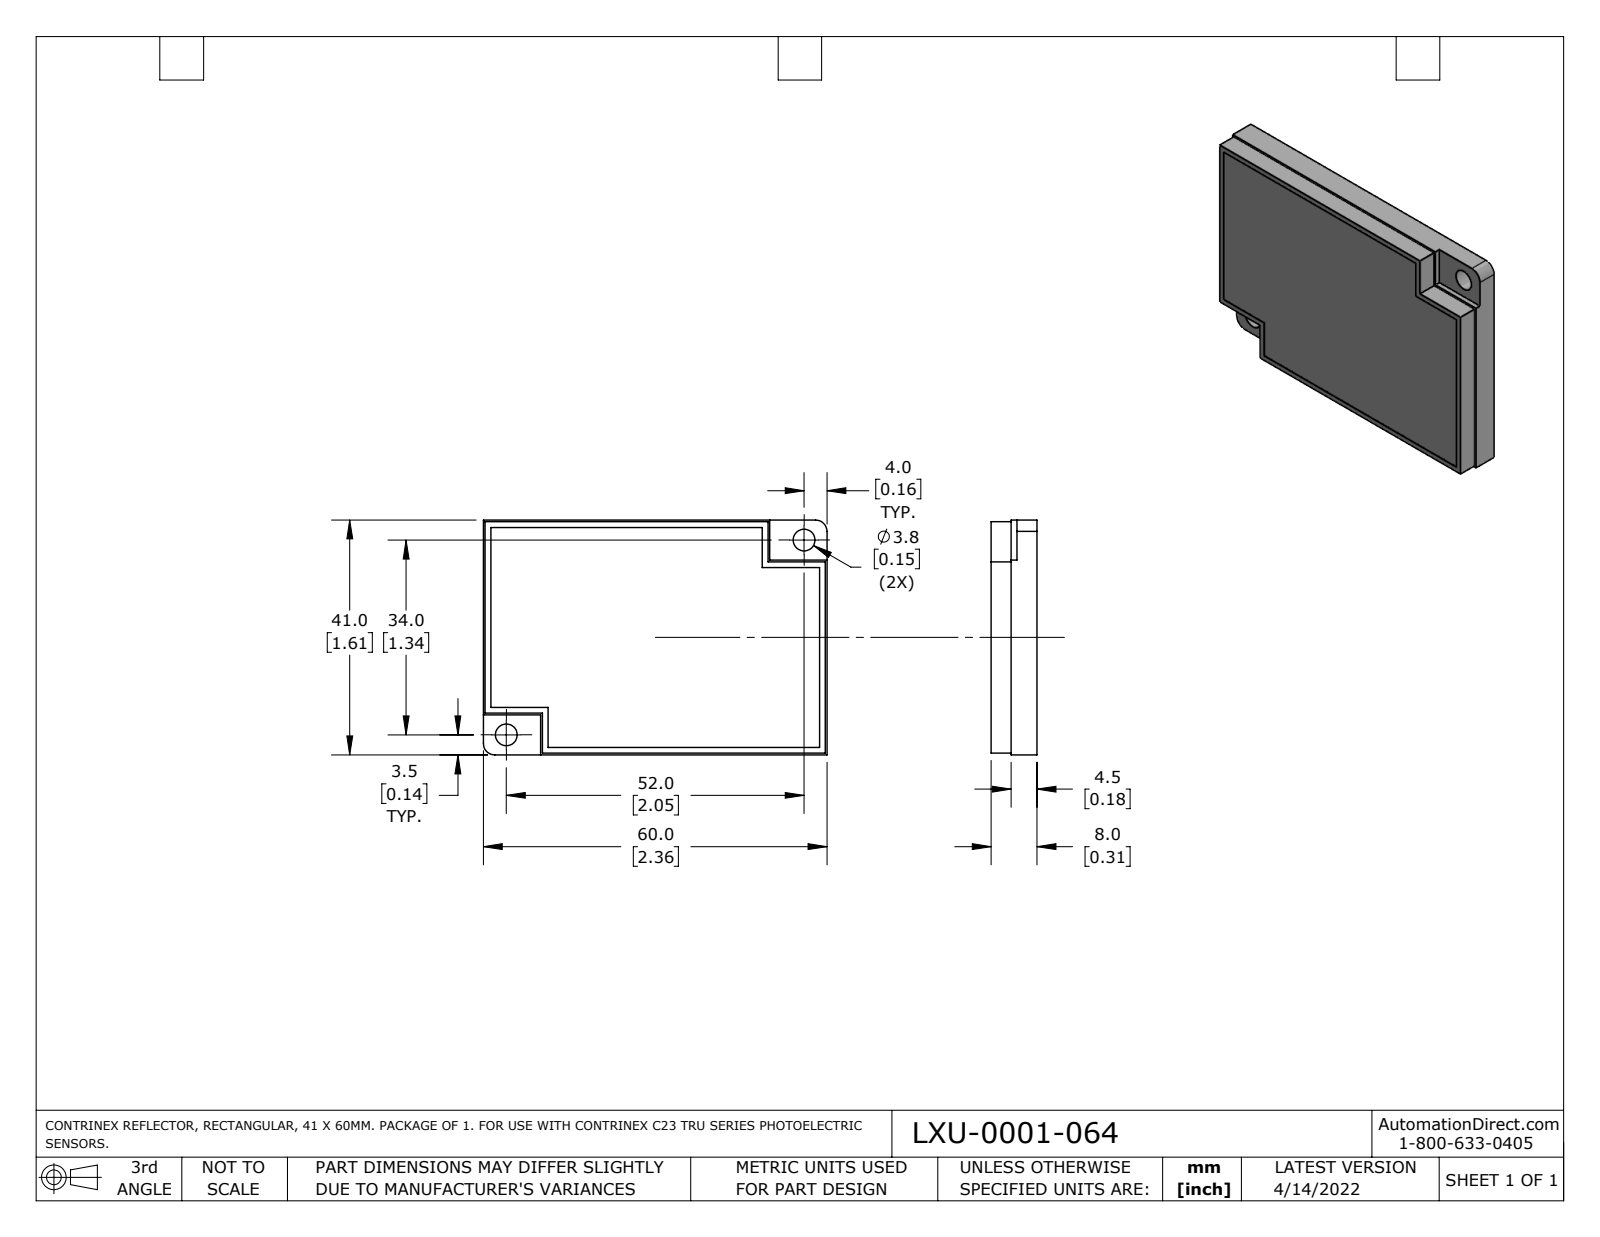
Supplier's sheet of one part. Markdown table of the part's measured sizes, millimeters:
| quantity | value |
| --- | --- |
| part name | LXU-0001-064 |
| STEP written by | PARTsolutions (AUTOMOTIVE_DESIGN) |
| units | millimeters |
| bodies | 1 solid, 34 faces (30 planar, 4 cylindrical, 0 other) |
| overall size | 60 × 41 × 8 |
| volume | 18 547 mm³ |
| surface area | 6 576 mm² |
| round holes (diameter × count) | 3.8 × 2 |
| partial cylindrical surfaces (radius × count) | 2 × 2 |
| main face-to-face distances | 7.9, 40.7, 41, 59.7, 8, 3.5, 4.5, 40.4, 60, 59.4 |
| hole center spacings | 62.13 |
